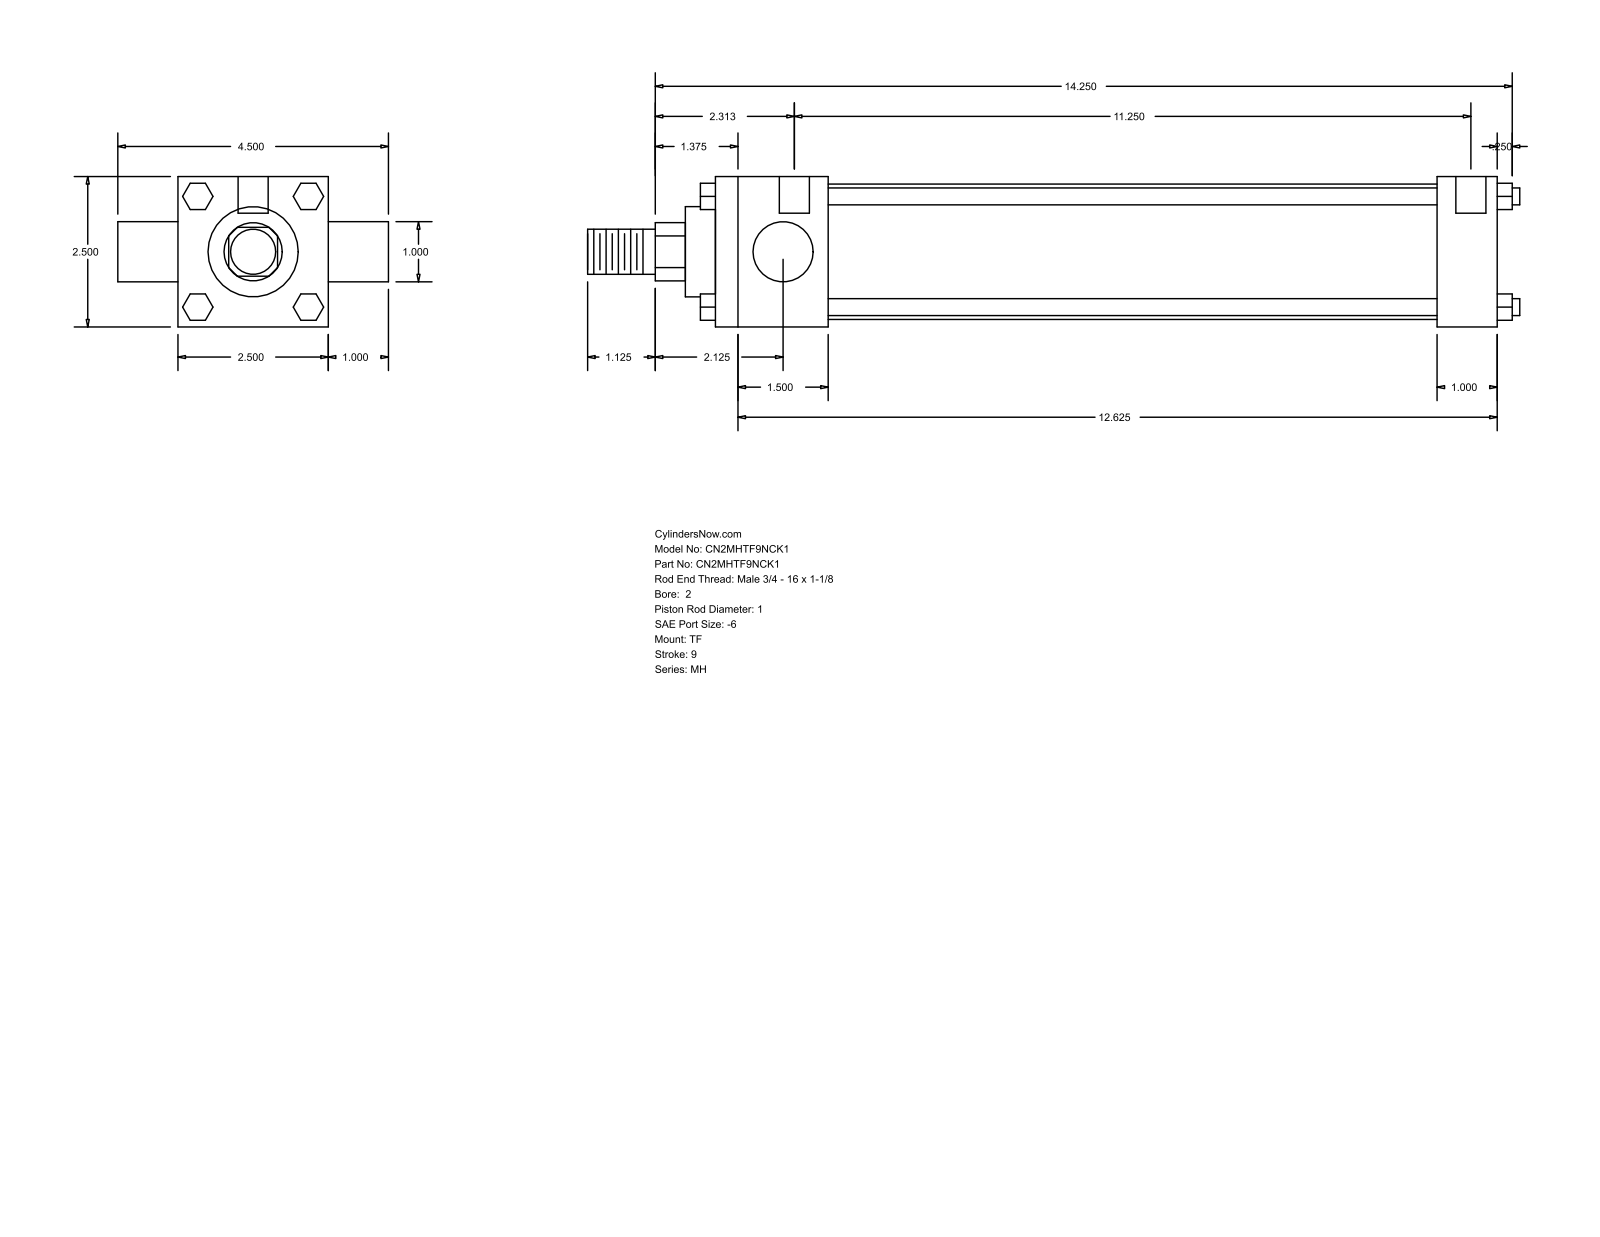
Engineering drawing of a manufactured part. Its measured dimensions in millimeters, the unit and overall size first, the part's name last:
Units: millimetres
Overall size (bounding box): 393.7 × 114.3 × 63.5
Round holes (diameter × count): ⌀5.56 ×3, ⌀12.7 ×2
Round bosses / shafts (diameter × count): ⌀7.14 ×4, ⌀25.4 ×2, ⌀57.15 ×1, ⌀38.1 ×1, ⌀19.05 ×1
Partial cylindrical surfaces — rounded edges, fillets, slot ends (radius × count): R12.29 ×1
Main face-to-face distances: 63.5, 330.2, 25.4, 47.63, 304.8, 257.17, 282.57, 88.9, 342.9, 6.35
Hole centre spacings: 3.17, 4.76, 285.75, 288.92, 290.51, 293.68
Bodies: 0 solids, 120 faces (92 planar, 28 cylindrical, 0 other)
Part name (STEP PRODUCT): MH_TF__0200_1
STEP written by: GSSL Pune (CONFIG_CONTROL_DESIGN)
